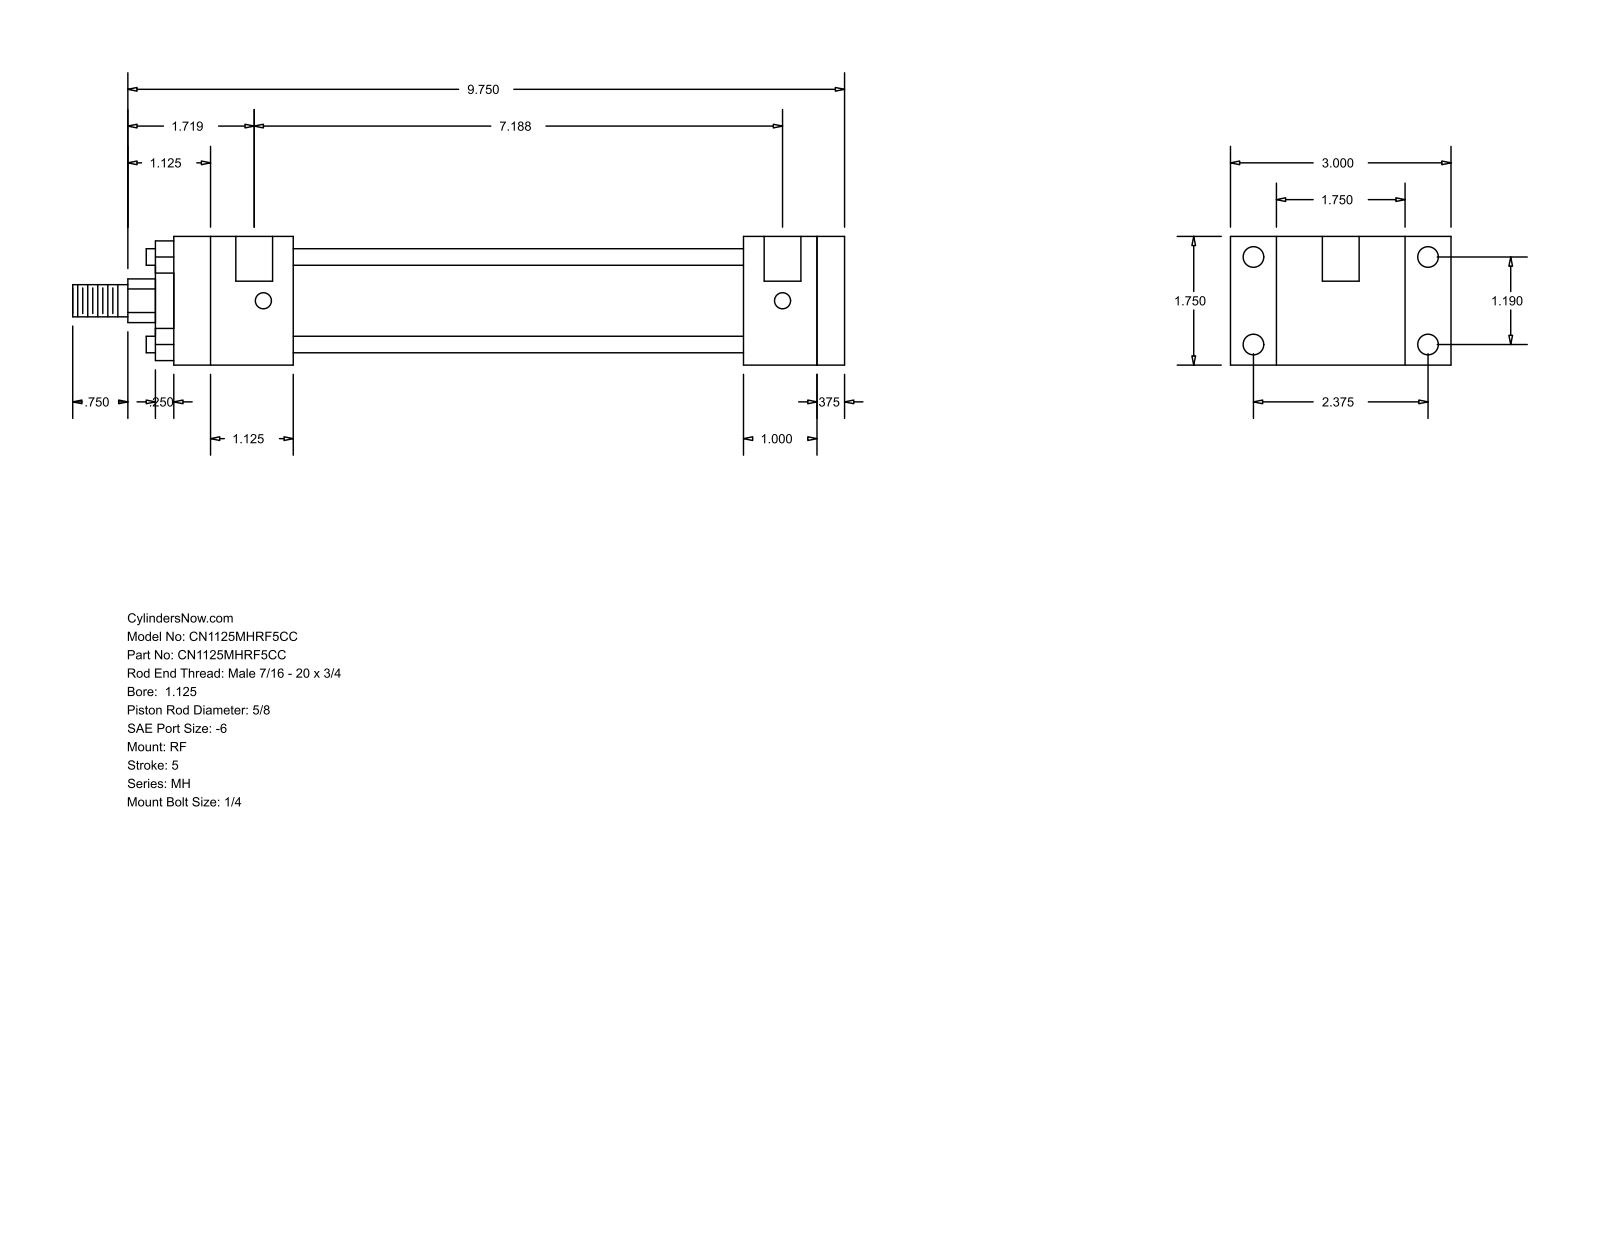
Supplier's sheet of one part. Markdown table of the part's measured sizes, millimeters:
| quantity | value |
| --- | --- |
| part name | MH_RF__0112_0.625 |
| STEP written by | GSSL Pune (CONFIG_CONTROL_DESIGN) |
| units | millimeters |
| bodies | 0 solids, 92 faces (64 planar, 28 cylindrical, 0 other) |
| overall size | 266.7 × 76.2 × 44.45 |
| round holes (diameter × count) | 5.56 × 4, 7.14 × 4, 12.7 × 2 |
| round bosses / shafts (diameter × count) | 5.71 × 4, 34.92 × 1, 28.57 × 1, 15.88 × 1, 11.11 × 1 |
| partial cylindrical surfaces (radius × count) | 7.54 × 1 |
| main face-to-face distances | 44.46, 9.53, 231.77, 25.4, 34.93, 15.87, 180.97, 190.5, 155.57, 41.27 |
| hole center spacings | 30.22, 60.32, 67.47, 179.39, 3.17, 182.56 |
